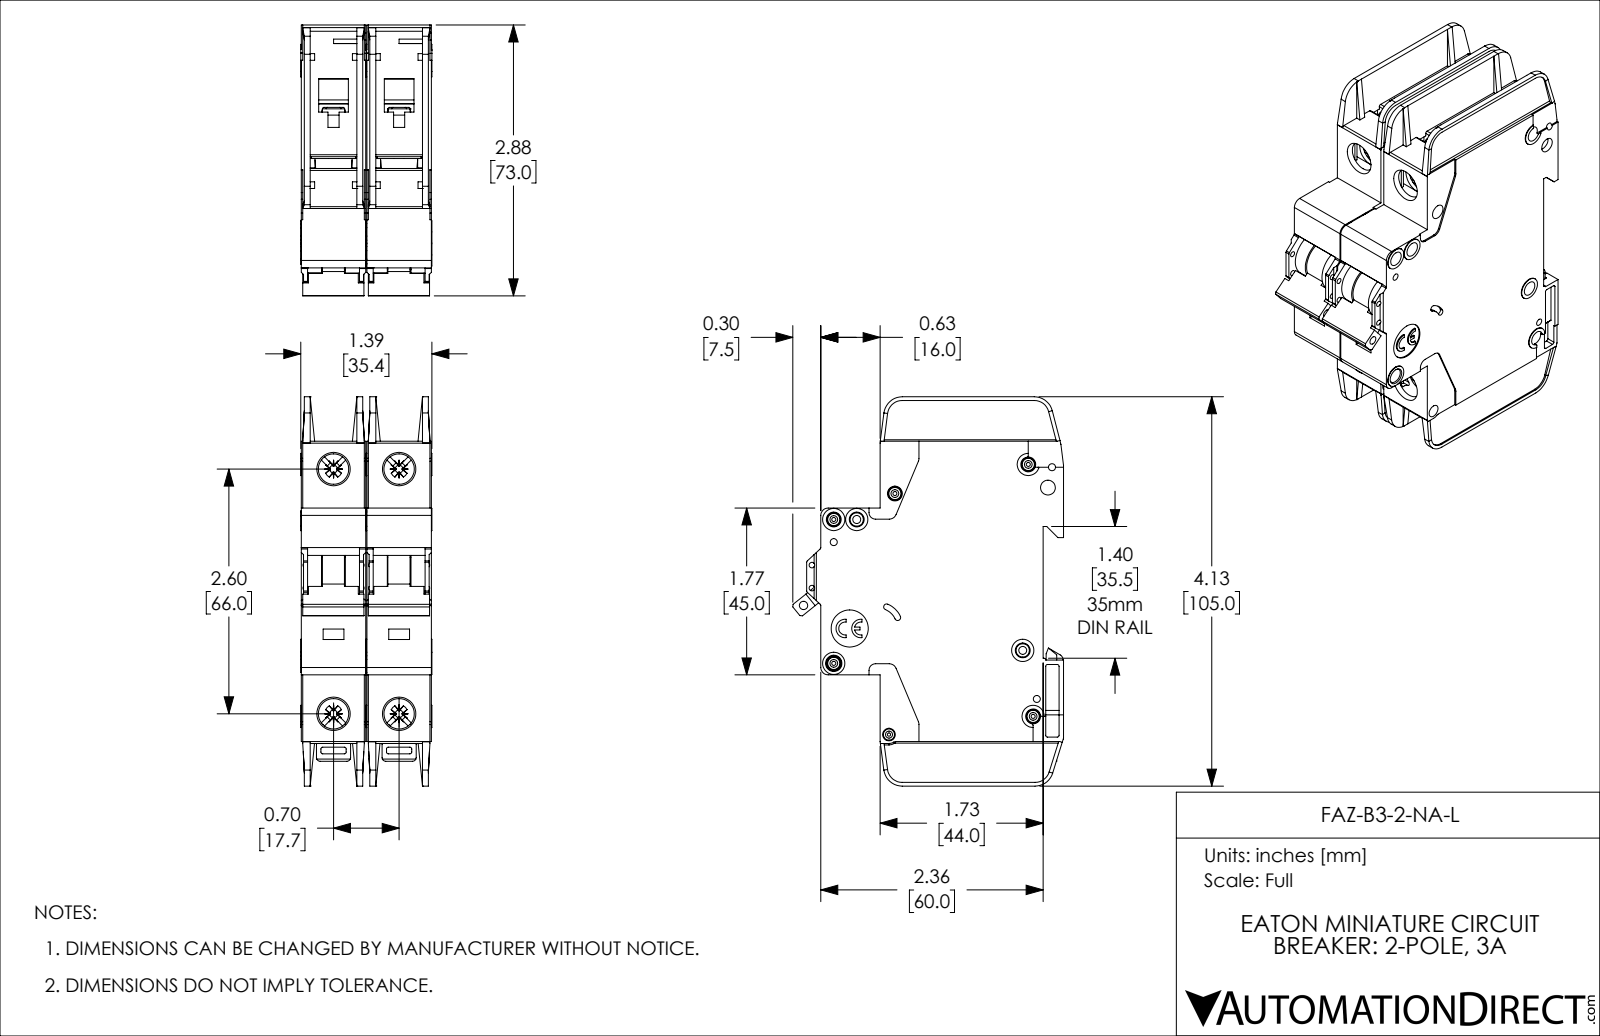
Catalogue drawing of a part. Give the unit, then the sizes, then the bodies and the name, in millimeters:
Units: millimetres
Overall size (bounding box): 105 × 73.1 × 35.4
Round holes (diameter × count): ⌀4 ×8, ⌀1.1 ×5, ⌀1.9 ×4, ⌀8.2 ×4, ⌀1.5 ×2, ⌀2.2 ×2, ⌀0.9 ×1, ⌀2.3 ×1, ⌀2.5 ×1, ⌀3.4 ×1, ⌀10 ×1
Round bosses / shafts (diameter × count): ⌀3.3 ×5, ⌀6 ×4, ⌀3 ×3, ⌀2.5 ×2
Partial cylindrical surfaces — rounded edges, fillets, slot ends (radius × count): R0.5 ×57, R0.4 ×20, R1 ×14, R2 ×10, R1.1 ×8, R0.2 ×5, R5 ×5, R0.3 ×4
Main face-to-face distances: 17.7, 1.2, 17.4, 15, 2.4, 16.2, 13.8, 35.1, 18.9, 16.5
Hole centre spacings: 6.2, 13.6, 17.7, 22.1, 66, 68.3, 4.8, 5.1
Volume: 153 500 mm³ · Surface area: 52 910 mm²
Bodies: 2 solids, 2254 faces (1342 planar, 714 cylindrical, 198 other)
Part name (STEP PRODUCT): FAZ-B3-2-NA-L
STEP written by: SolidWorks 2019 (AUTOMOTIVE_DESIGN)
